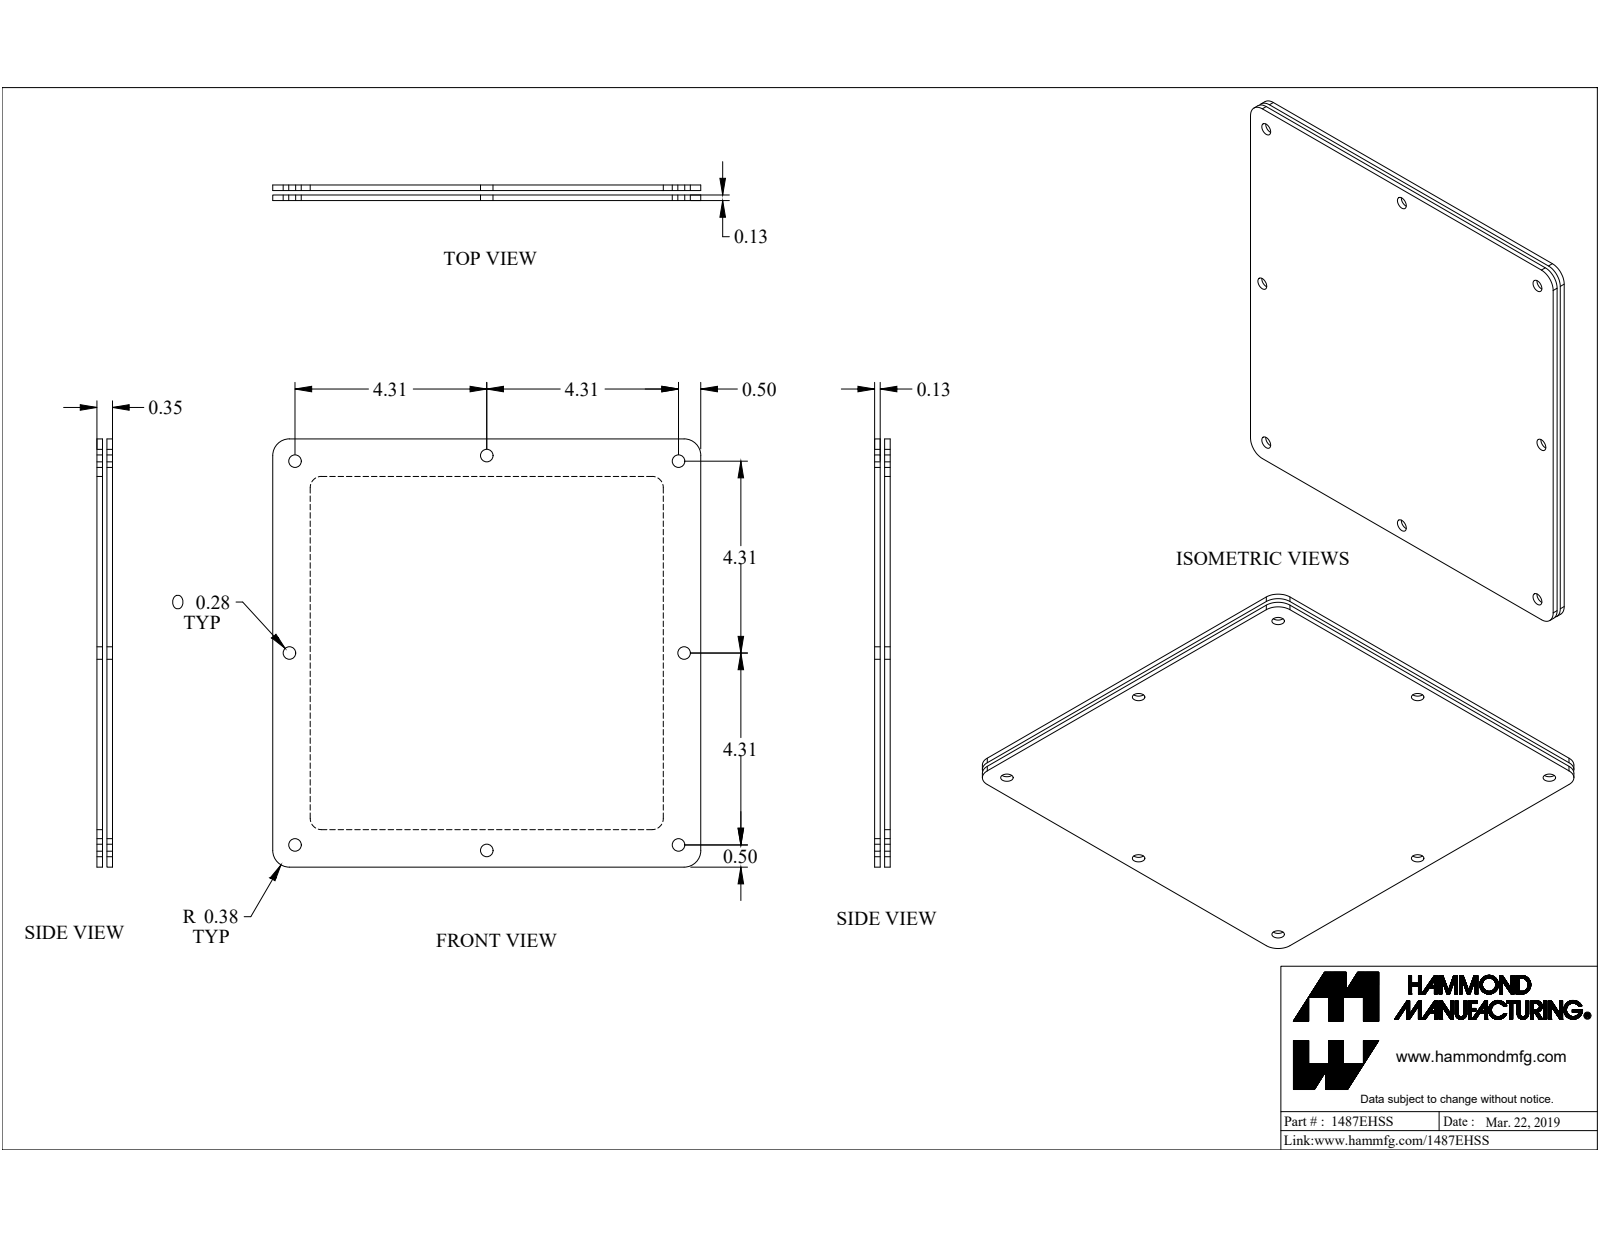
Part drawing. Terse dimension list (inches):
name: 1487EHSS
written by: SolidWorks 2019 (CONFIG_CONTROL_DESIGN)
unit: in
bodies: 5 solids, 131 faces (73 planar, 50 cylindrical, 8 other)
size: 9.625 × 9.625 × 0.971
volume: 15.22 in³; area: 259.6 in²
holes: 8× ⌀0.281, 1× ⌀0.196, 1× ⌀0.258, 1× ⌀0.35
bosses: 1× ⌀0.5, 1× ⌀0.25
rounds: 6× R0.02, 4× R0.25, 4× R0.375
face distances: 0.125, 0.125, 0.225, 0.1, 0.35, 0.225, 9.625, 0.843, 8.782, 7.939
hole spacings: 4.315, 9.755, 6.276, 8.625, 8.875, 12.198
